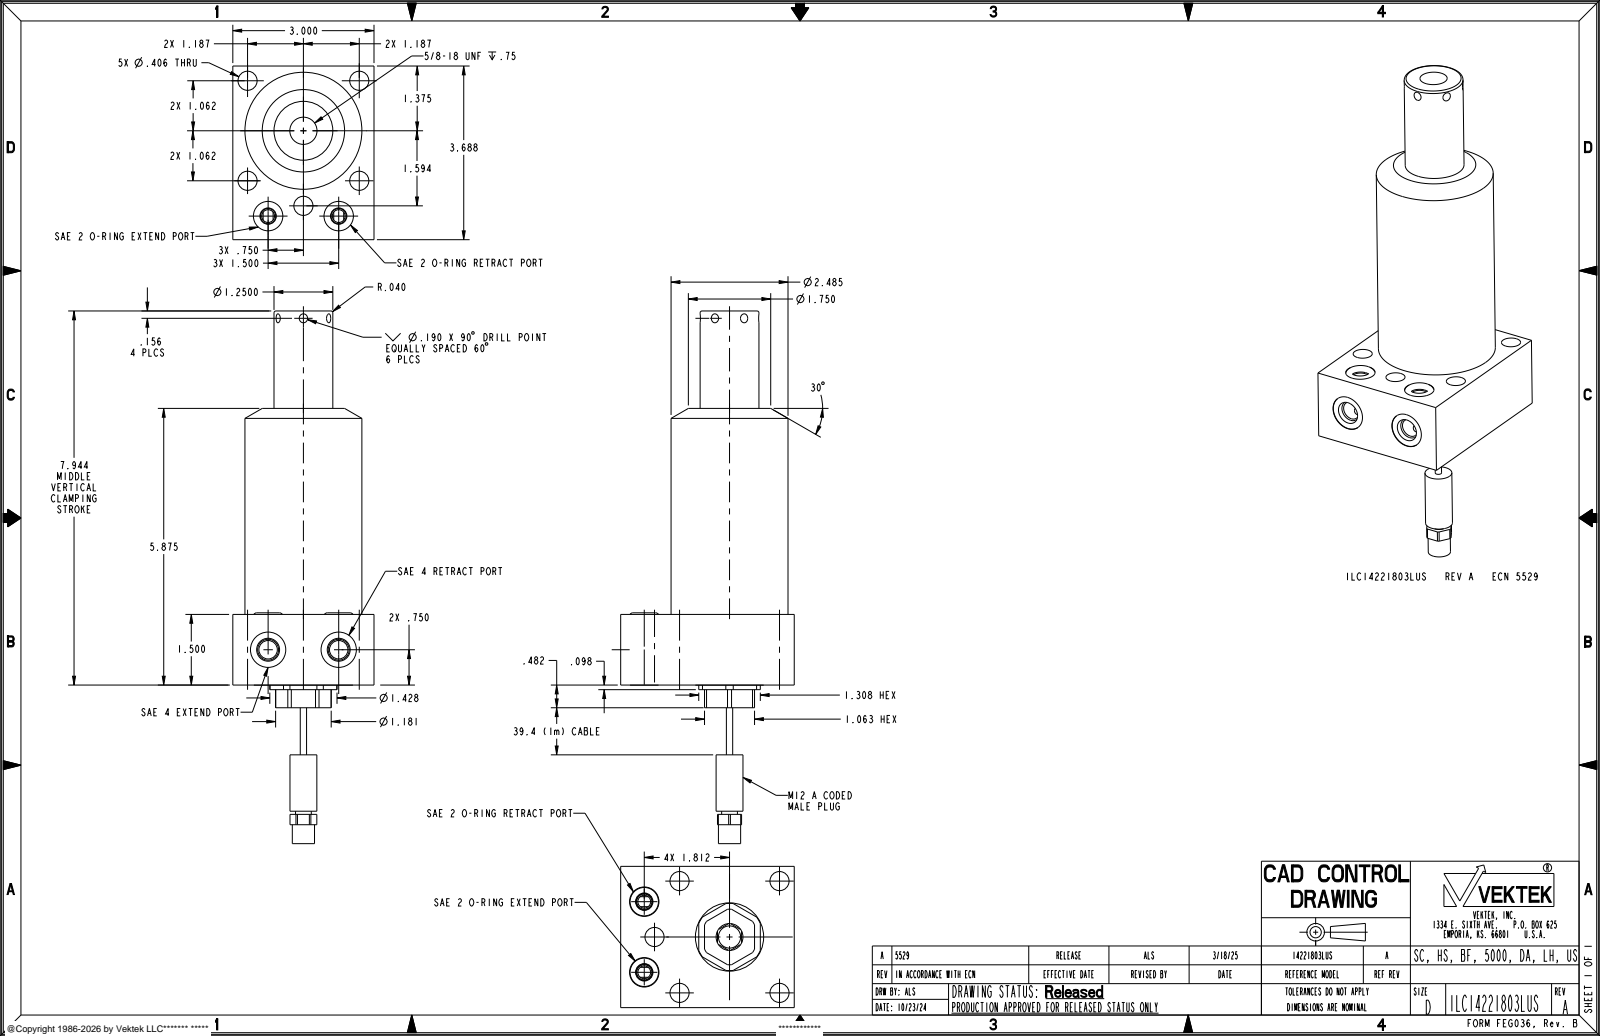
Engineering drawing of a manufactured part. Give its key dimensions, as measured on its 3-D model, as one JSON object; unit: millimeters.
{"part_name": "ILC14221803LUS", "step_written_by": "CREO PARAMETRIC BY PTC INC, 2021164 (AUTOMOTIVE_DESIGN)", "units": "millimeters", "bodies": {"solids": 5, "faces": 173, "planar": 49, "cylindrical": 70, "other": 54}, "overall_size": [287.3, 93.7, 76.2], "volume_mm3": 646000, "surface_area_mm2": 69290, "round_holes": [[10.3, 5], [6.9, 2], [10, 2], [15.9, 2], [19.1, 2], [14.7, 1]], "round_bosses_or_shafts": [[63.1, 1], [36.8, 1], [31.8, 1], [15.9, 1], [14.5, 1], [12, 1], [8.5, 1], [3.4, 1]], "partial_cylinders_radius": [[15, 1], [18.1, 1]], "face_to_face_distances": [76.2, 38.1, 93.7, 149.2, 111.1, 12.2, 50.3, 161.5, 2.7, 35.4], "hole_center_spacings": [40.5, 19.8, 22, 33, 38.1, 49.8, 52.8, 53.9]}
